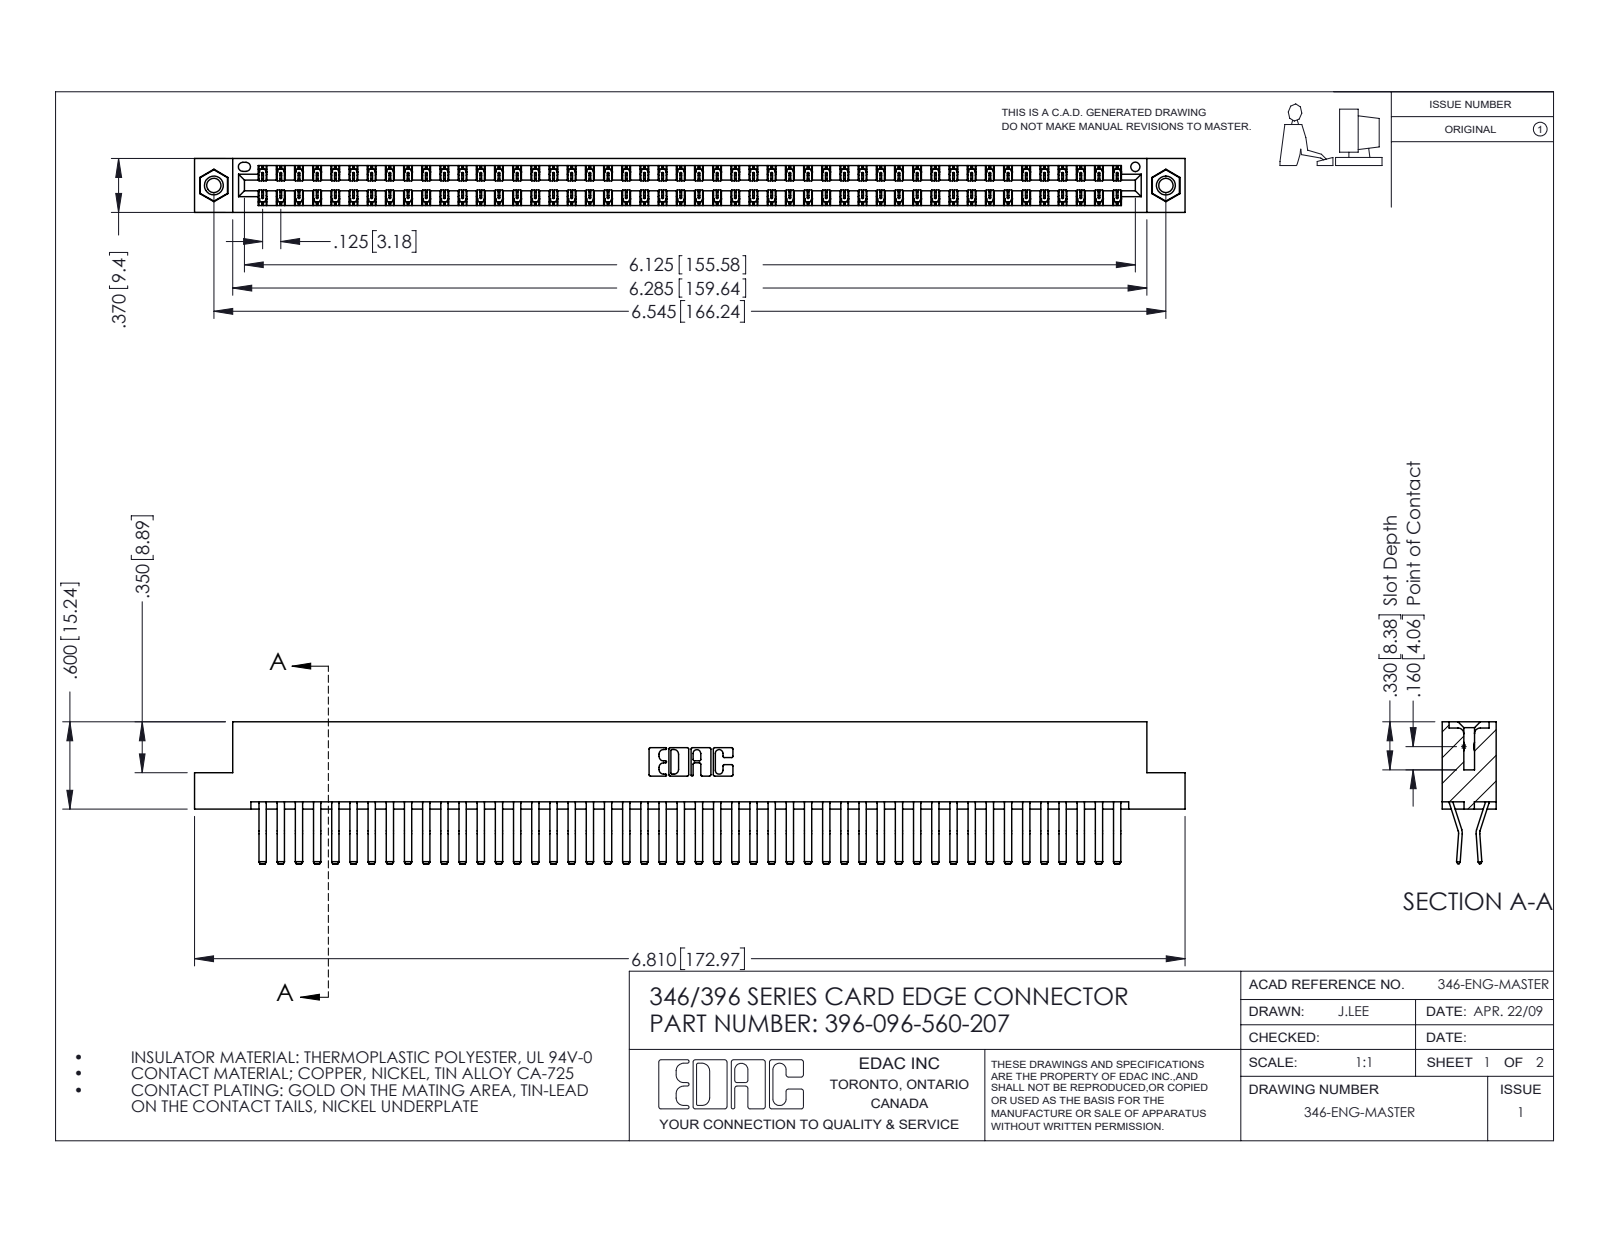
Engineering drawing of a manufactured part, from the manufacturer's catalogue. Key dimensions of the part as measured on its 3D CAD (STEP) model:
Part name (STEP PRODUCT): 346 Part_Flush Mounting Lugs - 0.156 Dia-TI; 345-250-001_345-250-005-103; 396-096-560-207; 345-292-001_560 Tail
STEP written by: SolidWorks 2016 (CONFIG_CONTROL_DESIGN)
Units: inches
Bodies: 99 solids, 5366 faces (3468 planar, 1882 cylindrical, 16 other)
Overall size (bounding box): 6.81 × 0.975 × 0.37
Volume: 1.07 in³ · Surface area: 40.15 in²
Round holes (diameter × count): ⌀0.098 ×2, ⌀0.125 ×2, ⌀0.156 ×2, ⌀0.064 ×1
Round bosses / shafts (diameter × count): ⌀0.155 ×2
Partial cylindrical surfaces — rounded edges, fillets, slot ends (radius × count): R0.006 ×144, R0.01 ×22, R0.007 ×6, R0.031 ×6, R0.026 ×3, R0.01 ×2, R0.014 ×2, R0.022 ×2
Main face-to-face distances: 0.048, 0.322, 0.37, 0.025, 0.25, 0.072, 0.298, 0.275, 0.148, 0.222
Hole centre spacings: 0.246, 6.336, 6.545
